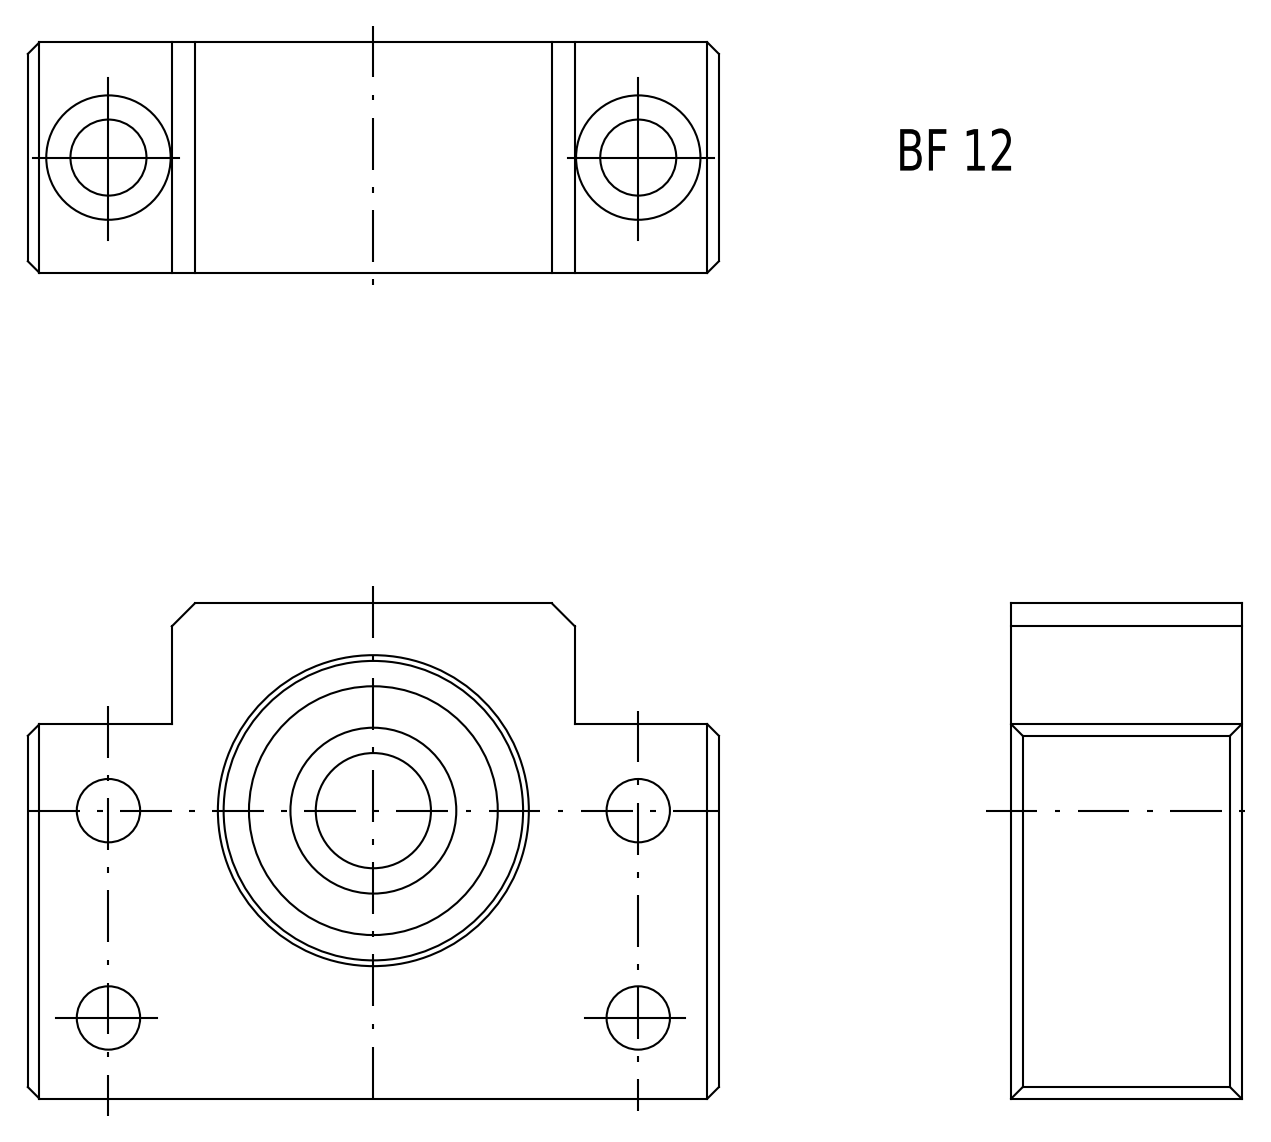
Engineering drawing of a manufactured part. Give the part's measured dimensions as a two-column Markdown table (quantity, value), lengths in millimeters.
| quantity | value |
| --- | --- |
| part name | BF12組合件 |
| STEP written by | SolidWorks 2008 (CONFIG_CONTROL_DESIGN) |
| units | millimeters |
| bodies | 13 solids, 222 faces (58 planar, 54 cylindrical, 110 other) |
| overall size | 60 × 43 × 20 |
| volume | 33 949 mm³ |
| surface area | 14 766 mm² |
| round holes (diameter × count) | 5.5 × 4, 6.6 × 2, 10.8 × 2, 10 × 1, 13.47 × 1, 20.65 × 1, 23.5 × 1, 26 × 1 |
| round bosses / shafts (diameter × count) | 14.65 × 1, 13.05 × 1 |
| main face-to-face distances | 20, 43, 60, 13, 6.1, 13.9, 47, 7, 6.6, 13.4 |
| hole center spacings | 46, 18, 23, 29.21, 49.4 |
